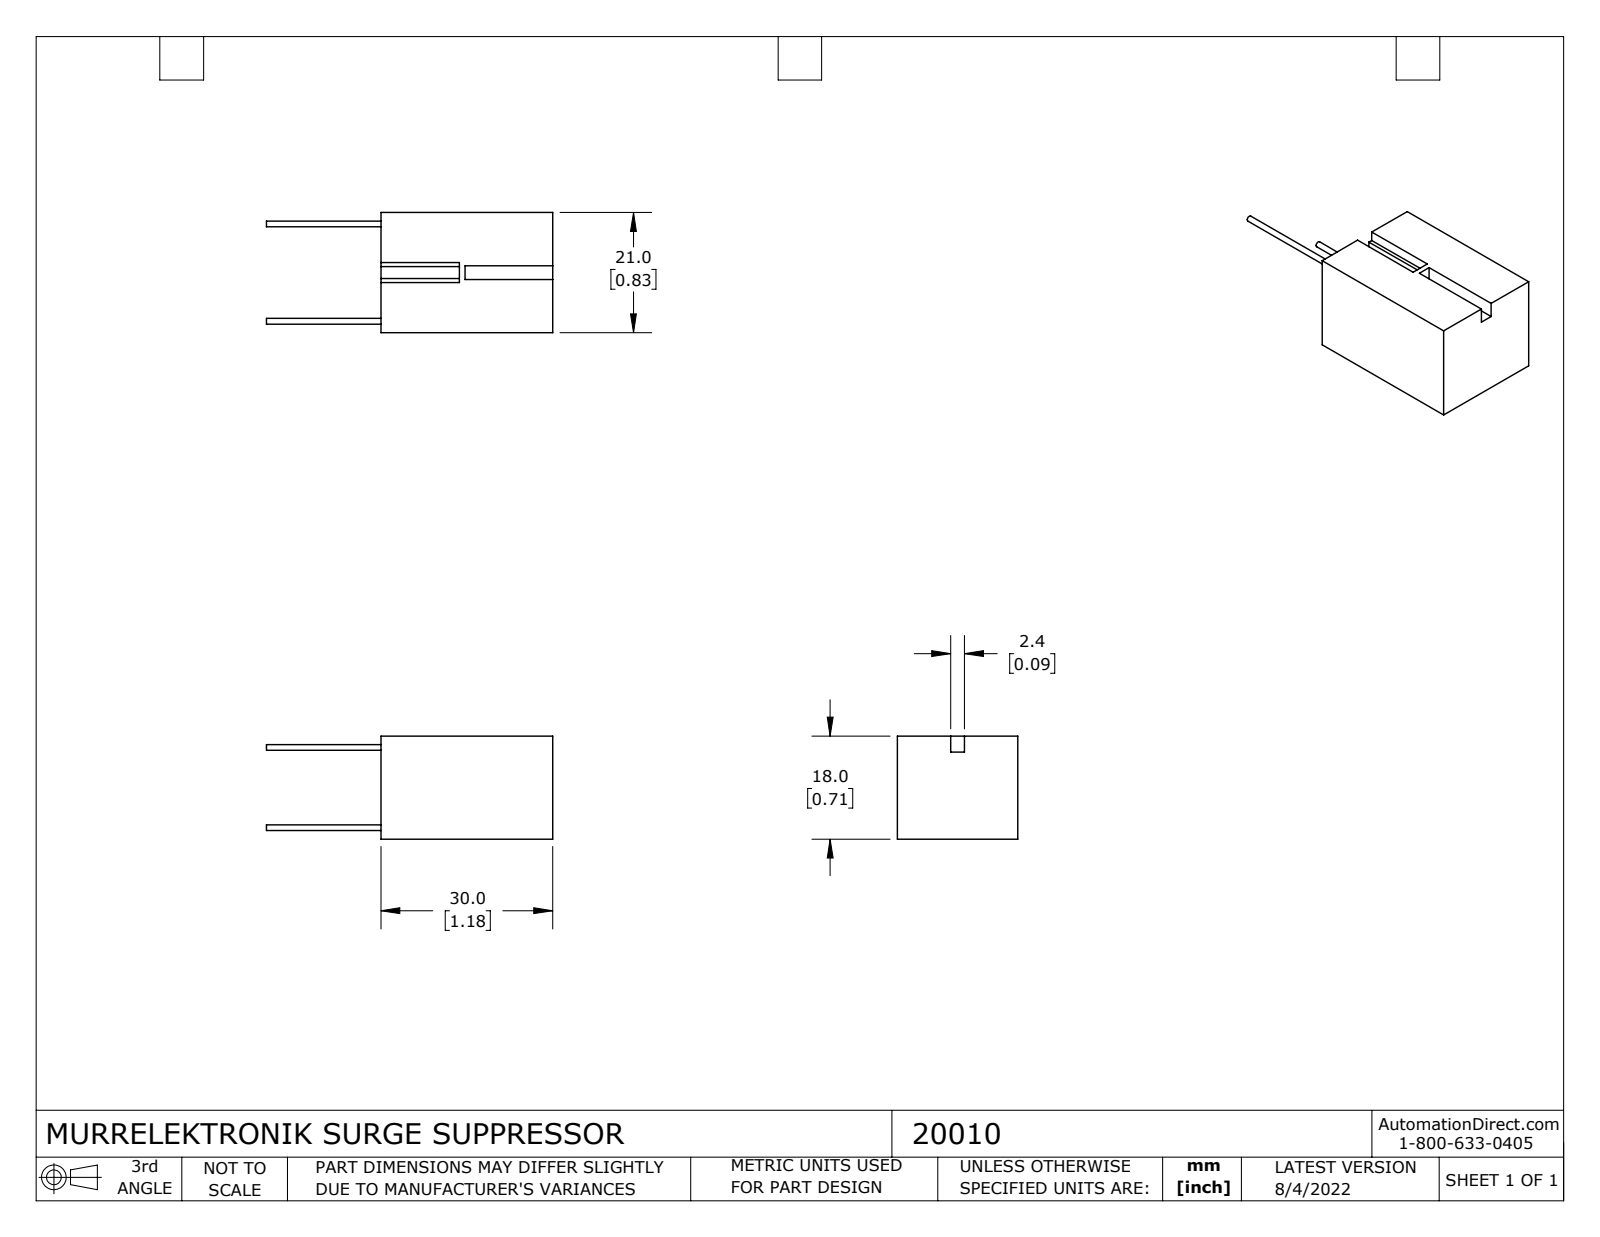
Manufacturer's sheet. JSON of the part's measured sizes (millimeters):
{"part_name": "20010", "step_written_by": "SolidWorks 2021 (CONFIG_CONTROL_DESIGN)", "units": "millimeters", "bodies": {"solids": 1, "faces": 24, "planar": 20, "cylindrical": 4, "other": 0}, "overall_size": [50, 21, 18], "volume_mm3": 11154, "surface_area_mm2": 3384, "round_bosses_or_shafts": [[1, 2]], "face_to_face_distances": [18, 21, 30, 2.8, 9.3, 11.7, 15.2, 8.75, 12.25, 0.55]}
